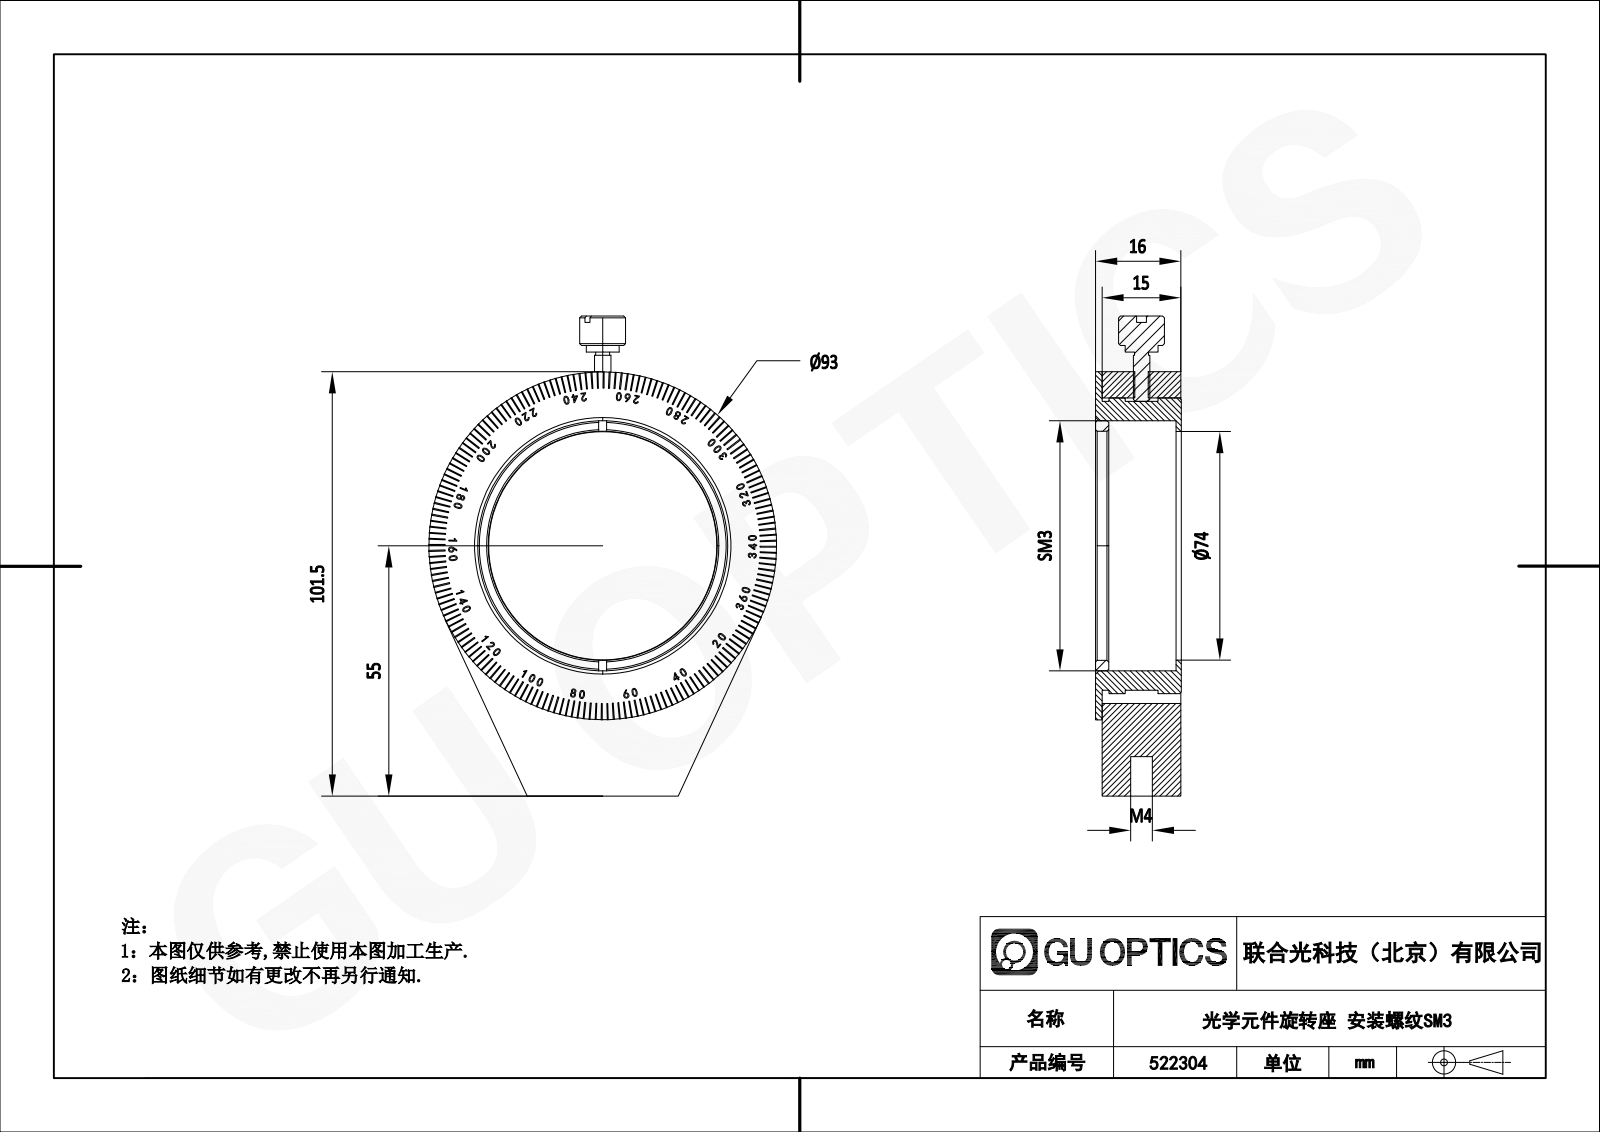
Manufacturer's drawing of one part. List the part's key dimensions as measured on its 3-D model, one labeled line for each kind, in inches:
Part name (STEP PRODUCT): 522304
STEP written by: SolidWorks 2020 (CONFIG_CONTROL_DESIGN)
Units: inches
Bodies: 4 solids, 2404 faces (1991 planar, 67 cylindrical, 346 other)
Overall size (bounding box): 4.28 × 3.661 × 0.63
Volume: 2.438 in³ · Surface area: 42.38 in²
Round holes (diameter × count): ⌀0.081 ×1, ⌀0.13 ×1, ⌀2.811 ×1, ⌀2.915 ×1, ⌀3.01 ×1, ⌀3.073 ×1
Round bosses / shafts (diameter × count): ⌀3.661 ×1, ⌀3.268 ×1, ⌀3.205 ×1, ⌀3.035 ×1, ⌀0.098 ×1, ⌀0.083 ×1
Partial cylindrical surfaces — rounded edges, fillets, slot ends (radius × count): R0.138 ×1, R1.555 ×1
Main face-to-face distances: 0.492, 0.138, 0.63, 0.039, 0.453, 0.098, 0.177, 0.315, 0.531, 0.591
